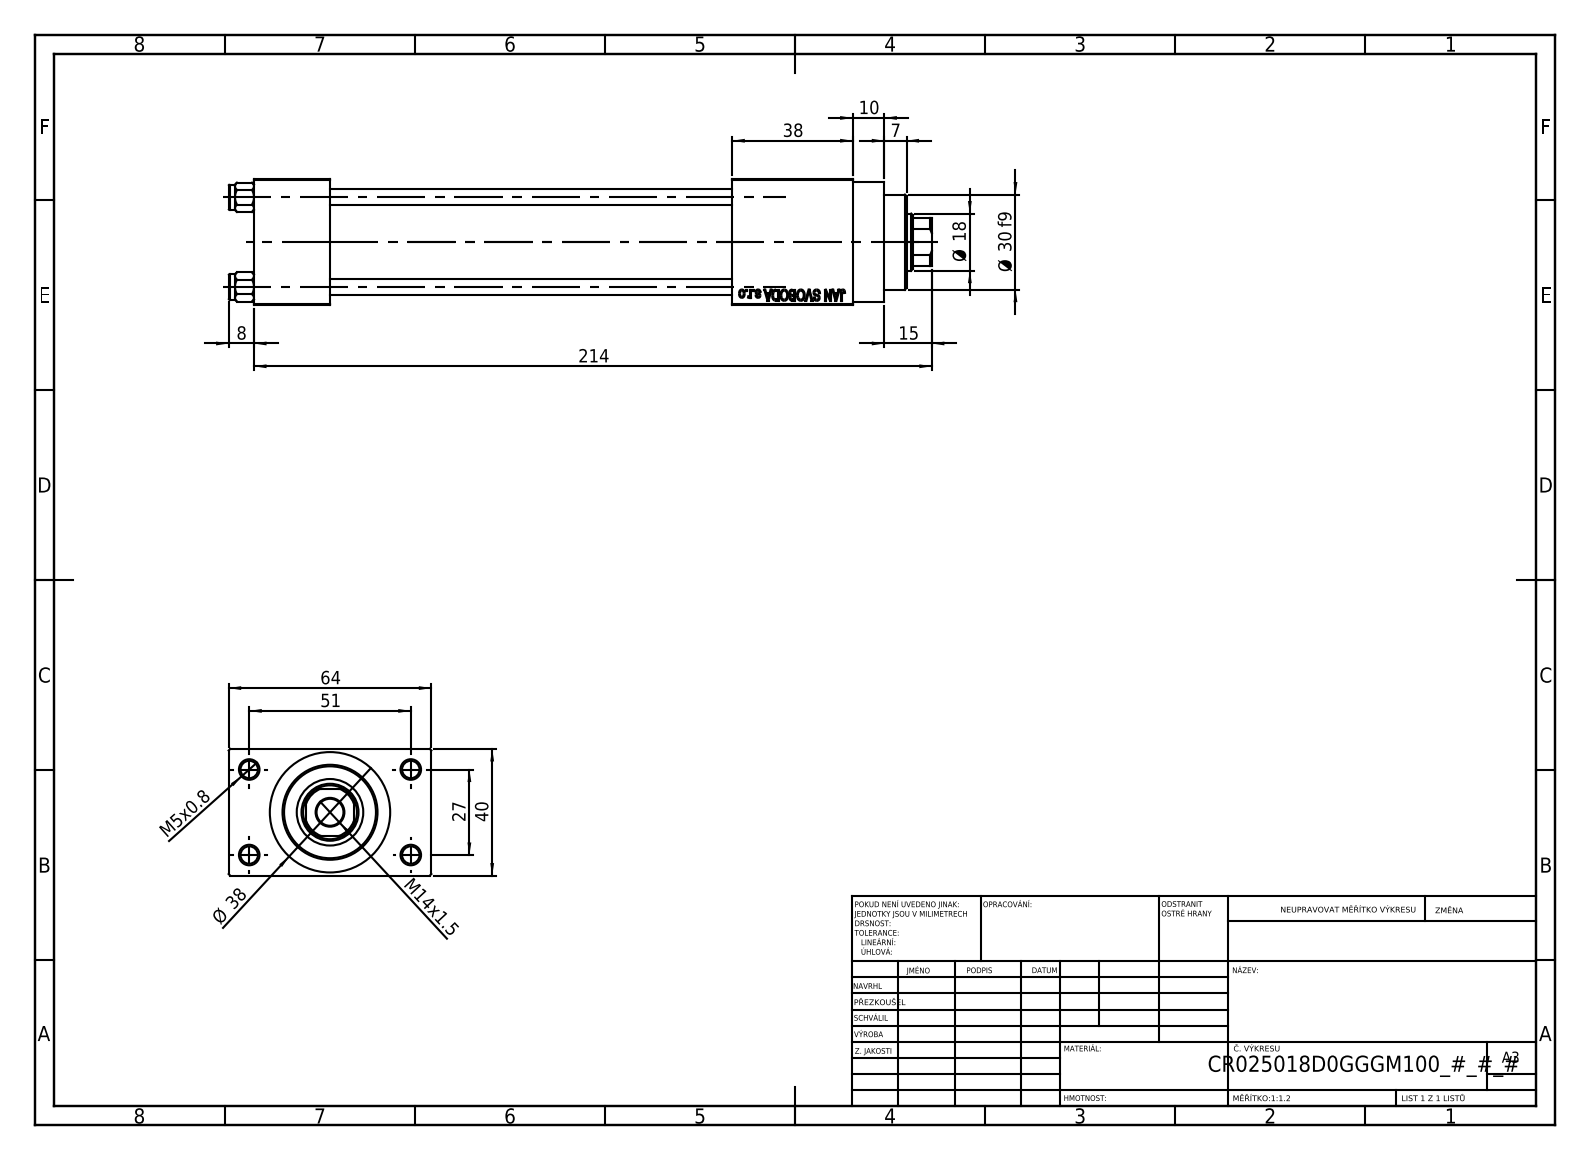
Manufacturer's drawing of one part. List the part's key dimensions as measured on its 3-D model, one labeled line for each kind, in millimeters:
Part name (STEP PRODUCT): V215CR_D_TYCINKA; NUT_M5_D; V215CR_VCP_D; V215CR_D_Body (+1 more)
STEP written by: SolidWorks 2019 (CONFIG_CONTROL_DESIGN)
Units: millimetres
Bodies: 11 solids, 1100 faces (495 planar, 87 cylindrical, 518 other)
Overall size (bounding box): 222 × 64 × 40
Volume: 228 536 mm³ · Surface area: 87 839 mm²
Round holes (diameter × count): ⌀5 ×4, ⌀5.5 ×4, ⌀20 ×3, ⌀7 ×2, ⌀13.16 ×2, ⌀8.5 ×1, ⌀18 ×1, ⌀21 ×1, ⌀25 ×1, ⌀30 ×1
Round bosses / shafts (diameter × count): ⌀8 ×4, ⌀38 ×1, ⌀31 ×1
Partial cylindrical surfaces — rounded edges, fillets, slot ends (radius × count): R8.5 ×1
Main face-to-face distances: 40, 12, 52, 127, 24, 151, 64, 38, 189, 165
Hole centre spacings: 11.37, 20.01, 28.3, 28.85, 29.89, 39.66, 48.34, 27
